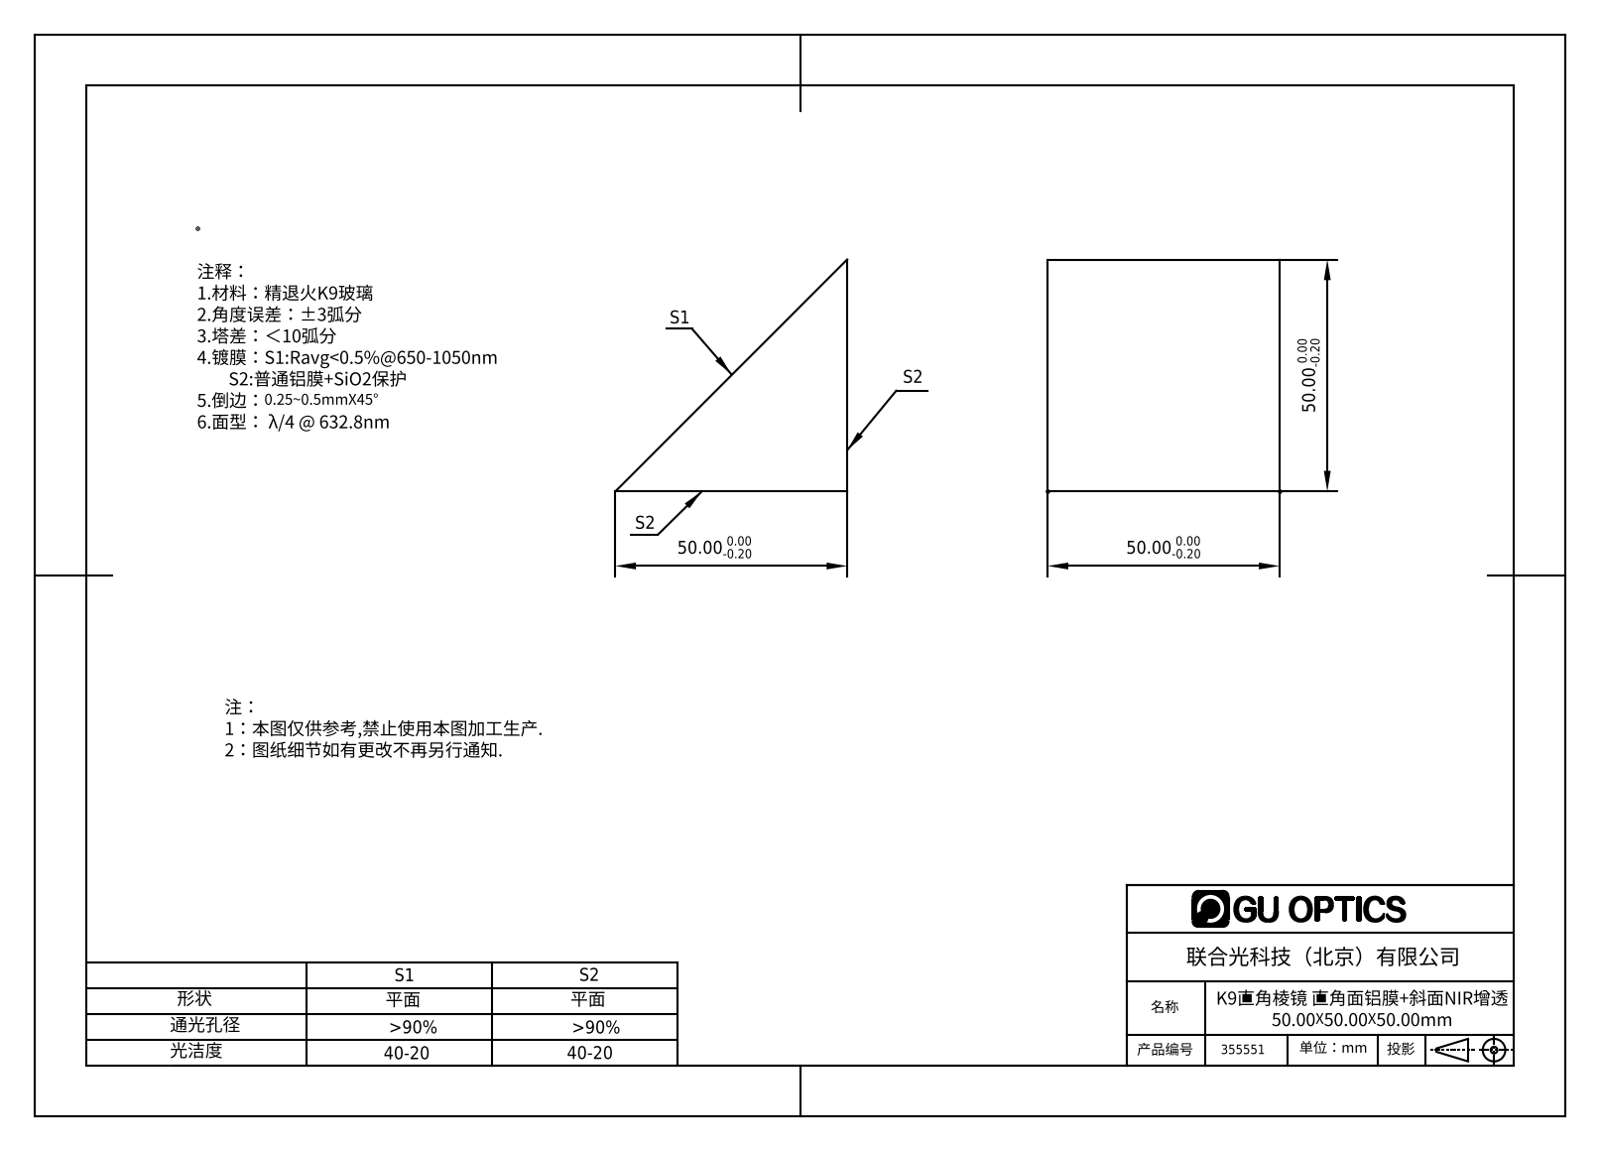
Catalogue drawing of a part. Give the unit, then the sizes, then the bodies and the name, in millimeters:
Units: millimetres
Overall size (bounding box): 50 × 50 × 50
Main face-to-face distances: 50
Volume: 62 500 mm³ · Surface area: 11 036 mm²
Bodies: 1 solid, 5 faces (5 planar, 0 cylindrical, 0 other)
Part name (STEP PRODUCT): 355511
STEP written by: SolidWorks 2016 (CONFIG_CONTROL_DESIGN)
